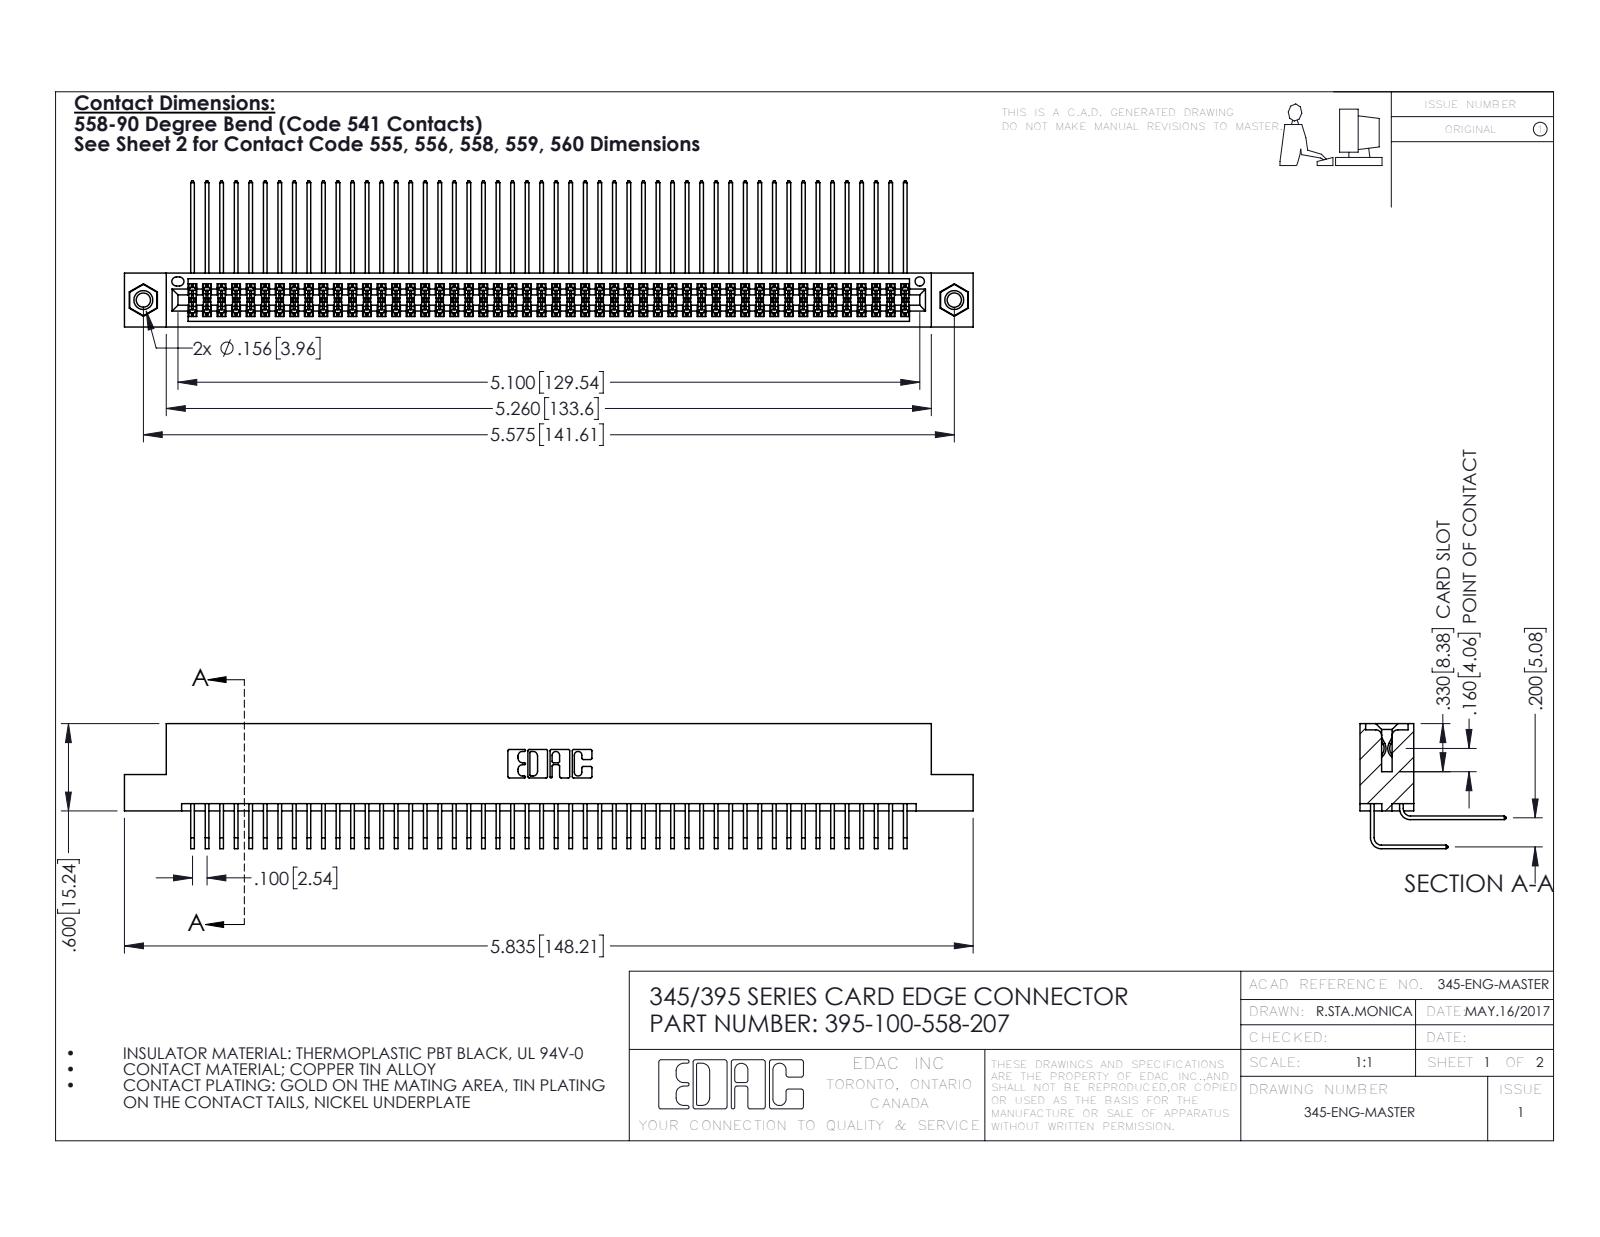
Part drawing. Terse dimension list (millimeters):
name: 345 Part_Flush Mounting Lugs - 0.156 Dia-TI; 345-250-001_345-250-005-103; 345-292-001_558 559 Tail - 1; 395-100-558-207 (+1 more)
written by: SolidWorks 2016 (CONFIG_CONTROL_DESIGN)
unit: mm
bodies: 103 solids, 5386 faces (3612 planar, 1758 cylindrical, 16 other)
size: 148.2 × 25.5 × 21.8
volume: 15 000 mm³; area: 25 120 mm²
holes: 2× ⌀2.5, 2× ⌀3.2, 2× ⌀4, 1× ⌀1.6
bosses: 2× ⌀3.9
rounds: 151× R0.2, 22× R0.3, 6× R0.2, 6× R0.8, 3× R0.7, 2× R0.4, 2× R0.5, 2× R0.6
face distances: 1.8, 7.6, 5.1, 9.4, 2.5, 6.9, 0.6, 5.7, 0.6, 4.4
hole spacings: 6.9, 135.6, 141.6
